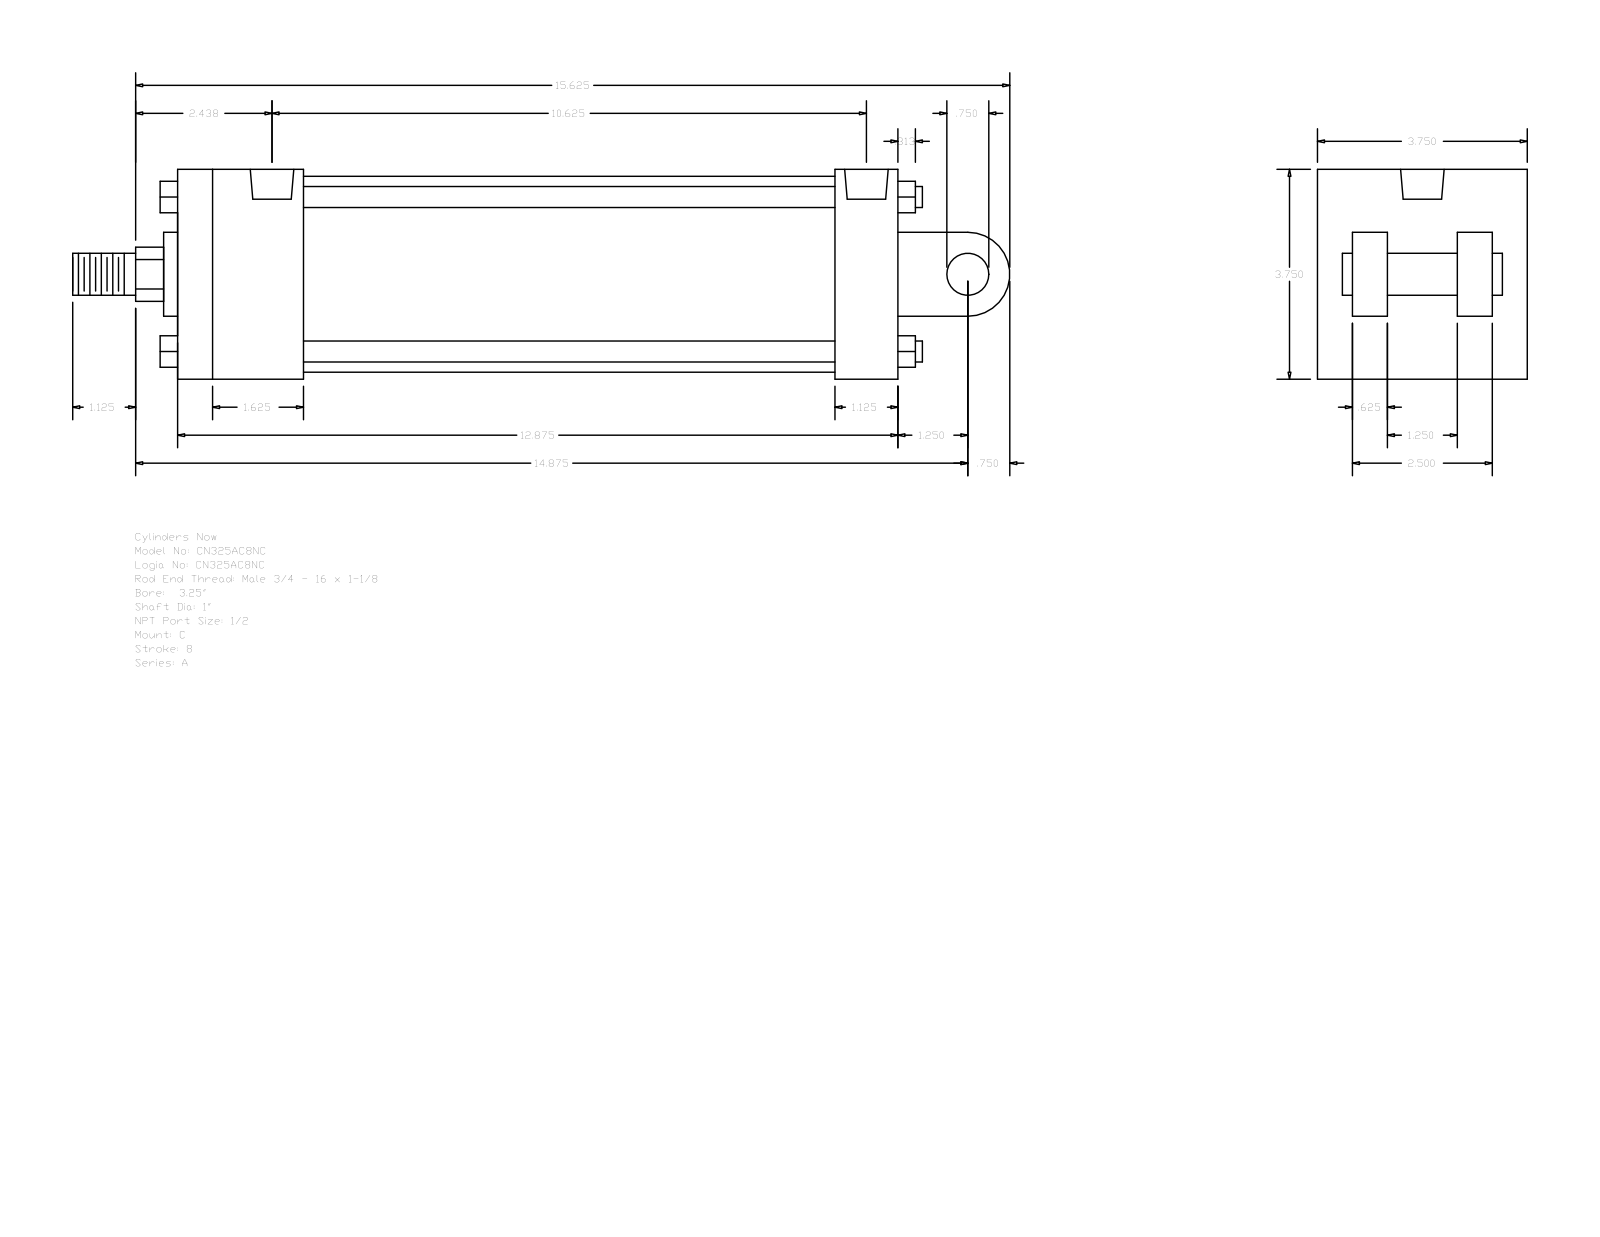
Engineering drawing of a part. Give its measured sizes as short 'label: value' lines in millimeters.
name: A_C__0325_1
written by: GSSL Pune (CONFIG_CONTROL_DESIGN)
unit: mm
bodies: 0 solids, 135 faces (102 planar, 33 cylindrical, 0 other)
size: 425.45 × 95.25 × 95.25
holes: 4× ⌀8.73, 2× ⌀19.77
bosses: 4× ⌀9.53, 2× ⌀19.05, 1× ⌀88.9, 1× ⌀38.1, 1× ⌀25.4
rounds: 1× R12.29, 1× R19.05
face distances: 95.24, 327.02, 15.87, 63.5, 28.57, 79.37, 31.74, 47.63, 66.67, 298.45
hole spacings: 3.18, 263.52, 266.7, 269.88
